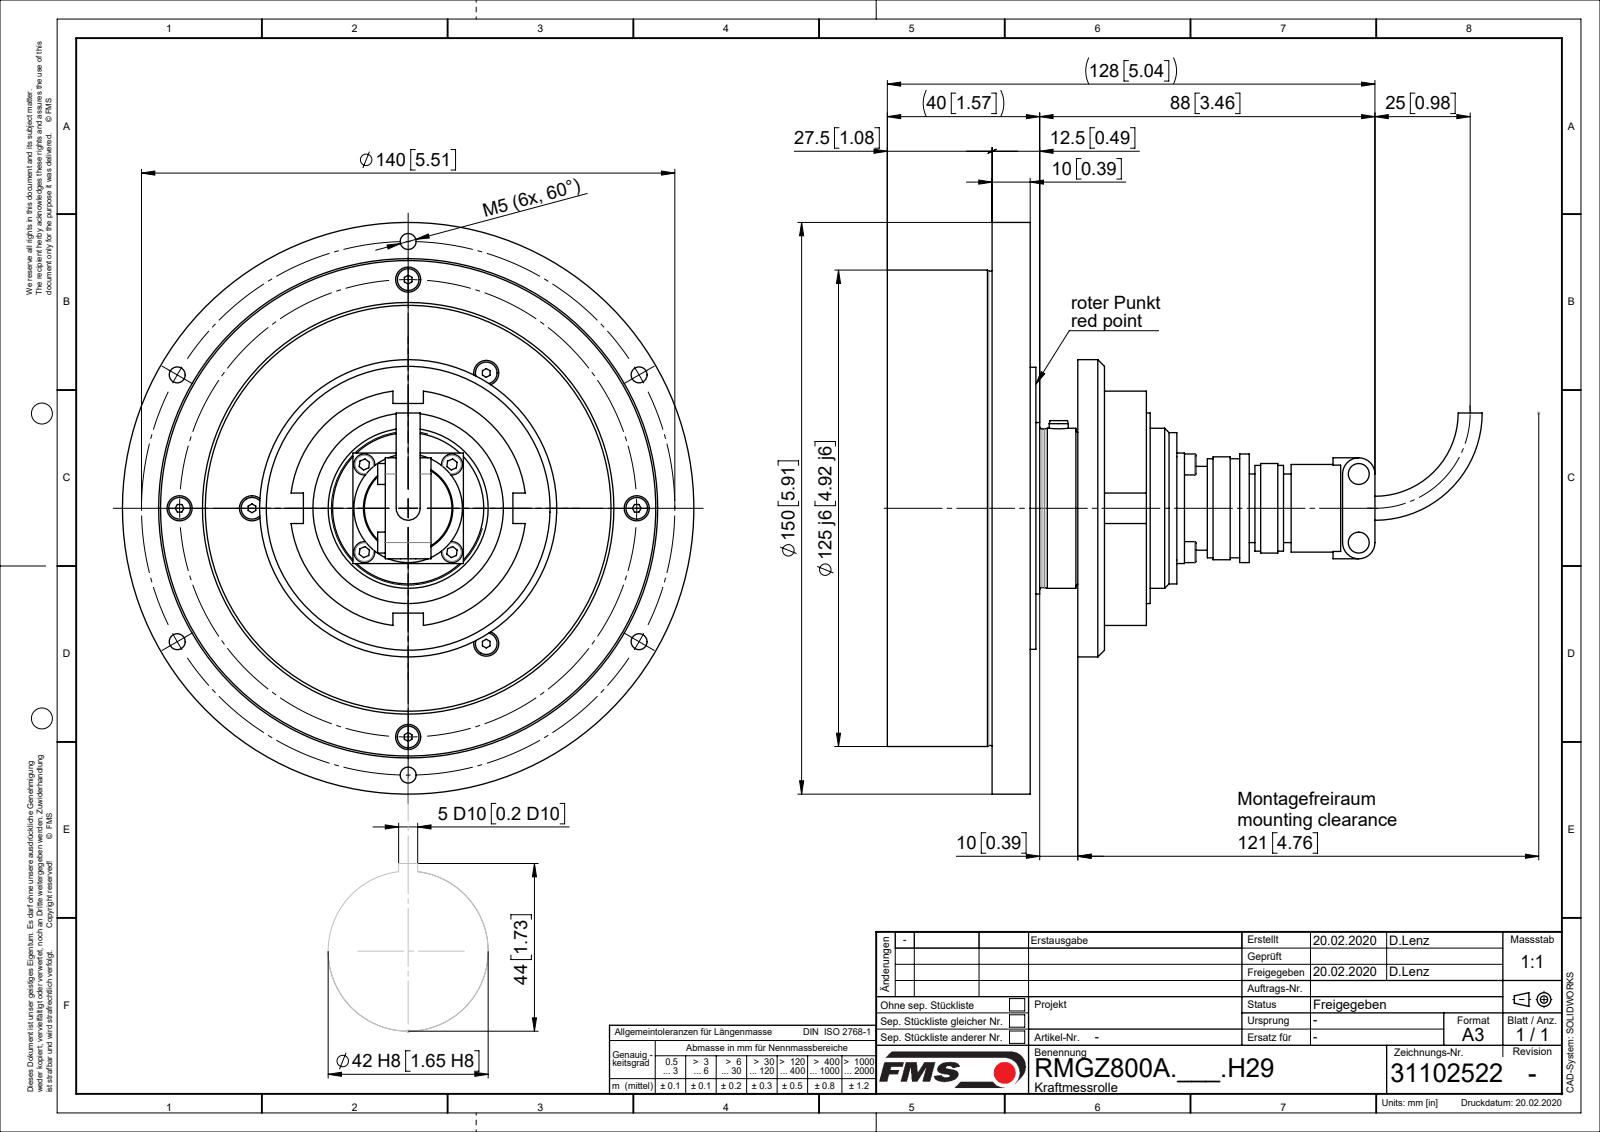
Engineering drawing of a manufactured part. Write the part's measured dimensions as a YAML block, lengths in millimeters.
part_name: "R50563; R4753004; TEIL1; R47533 (+8 more)"
step_written_by: "Mechanical Desktop 2009 (CONFIG_CONTROL_DESIGN)"
units: millimeters
bodies: {solids: 24, faces: 561, planar: 171, cylindrical: 250, other: 140}
overall_size: [156.15, 150, 150]
volume: 559380
surface_area: 205831
round_holes:
  - {diameter: 2.6, count: 11}
  - {diameter: 3.4, count: 11}
  - {diameter: 4.33, count: 6}
  - {diameter: 16, count: 5}
  - {diameter: 4, count: 1}
  - {diameter: 5, count: 1}
  - {diameter: 6, count: 1}
  - {diameter: 8, count: 1}
  - {diameter: 23, count: 1}
  - {diameter: 32.2, count: 1}
  - {diameter: 37.8, count: 1}
  - {diameter: 43, count: 1}
round_bosses_or_shafts:
  - {diameter: 3, count: 11}
  - {diameter: 6, count: 7}
  - {diameter: 5.5, count: 6}
  - {diameter: 2.5, count: 4}
  - {diameter: 150, count: 1}
  - {diameter: 125, count: 1}
  - {diameter: 115, count: 1}
  - {diameter: 106.5, count: 1}
partial_cylinders:
  - {radius: 4.25, count: 2}
  - {radius: 27, count: 1}
  - {radius: 29, count: 1}
face_to_face_distances: [2, 4, 30, 32, 13, 35.5, 37.5, 25.5, 31.5, 29.5]
hole_center_spacings: [70, 49.84, 72.42, 121.24, 40.12, 81.12, 16.26, 20.11]
